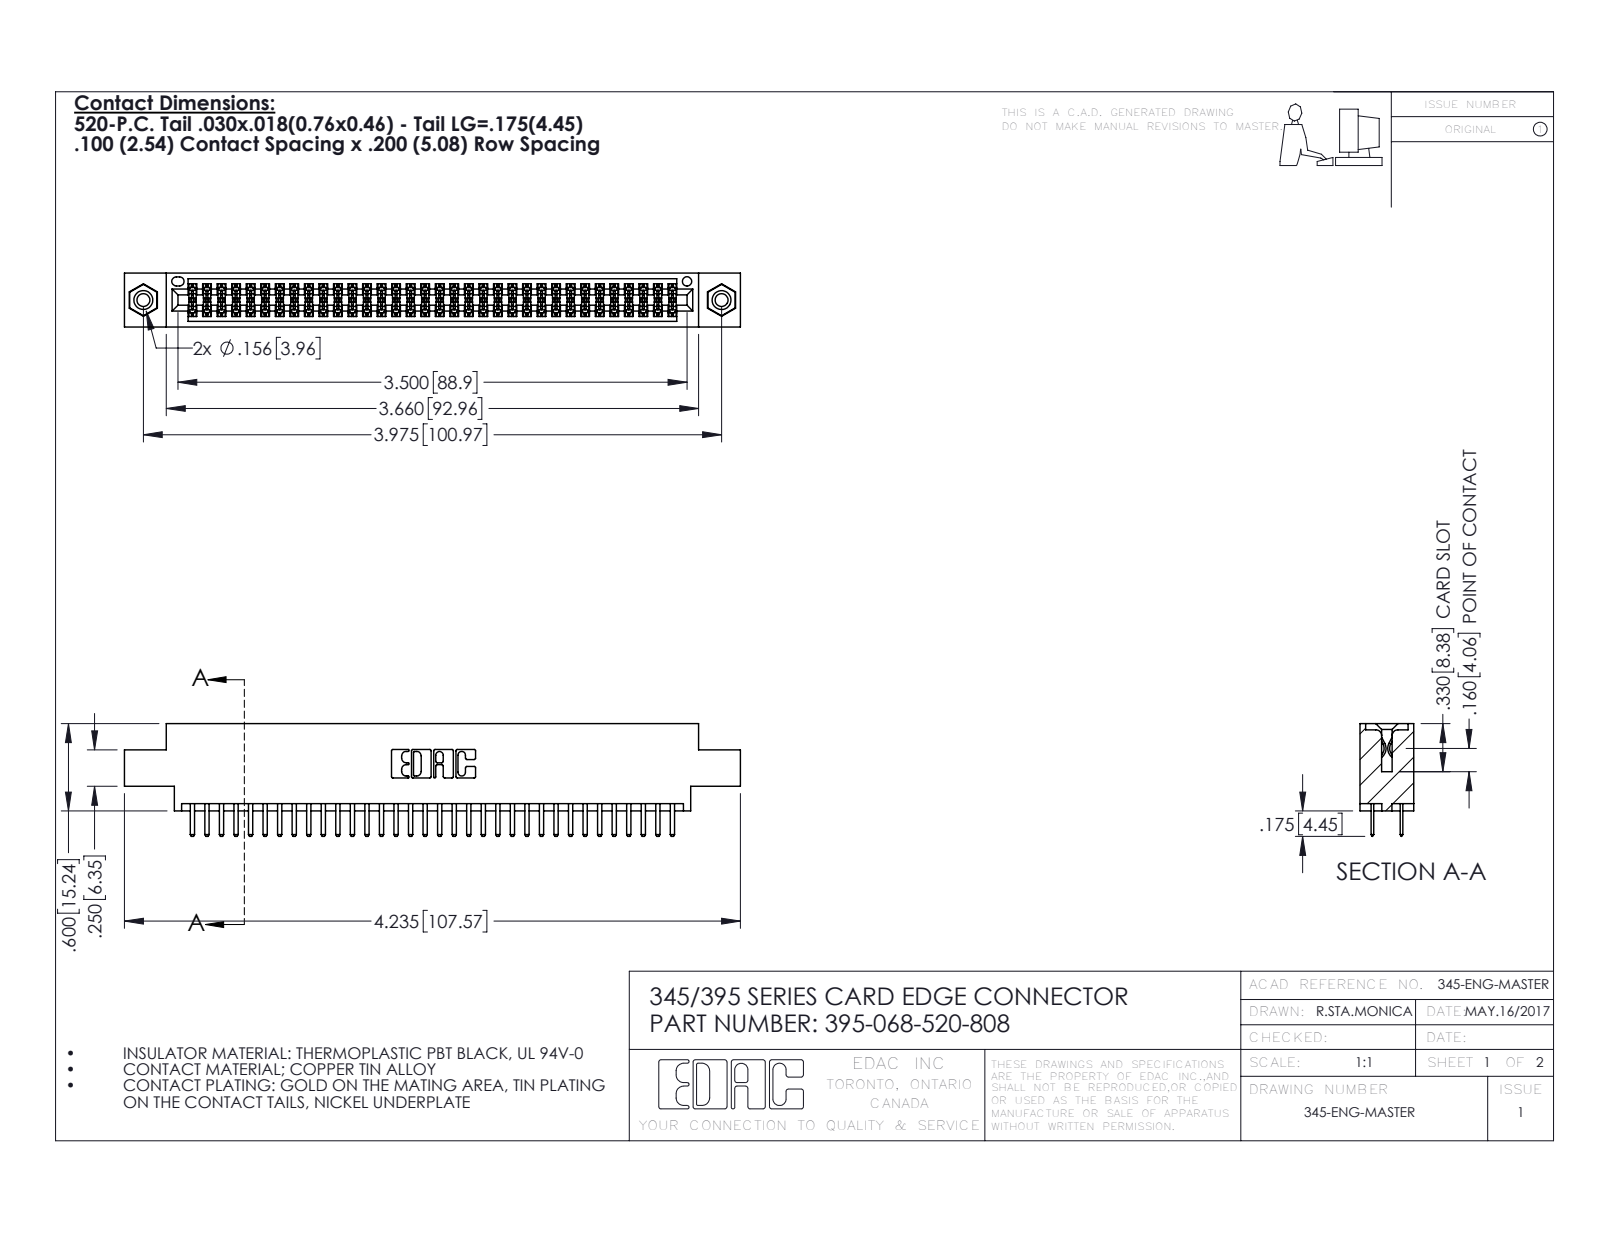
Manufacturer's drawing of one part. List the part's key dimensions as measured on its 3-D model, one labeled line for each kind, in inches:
Part name (STEP PRODUCT): 345 Part_0.170 Offset - 0.156 Dia-TI; 345-250-001_345-250-003-102; 395-068-520-808; 345-292-001_345-293-120
STEP written by: SolidWorks 2016 (CONFIG_CONTROL_DESIGN)
Units: inches
Bodies: 71 solids, 3862 faces (2496 planar, 1350 cylindrical, 16 other)
Overall size (bounding box): 4.235 × 0.775 × 0.37
Volume: 0.624 in³ · Surface area: 23.33 in²
Round holes (diameter × count): ⌀0.089 ×2, ⌀0.125 ×2, ⌀0.156 ×2, ⌀0.064 ×1
Round bosses / shafts (diameter × count): ⌀0.155 ×2
Partial cylindrical surfaces — rounded edges, fillets, slot ends (radius × count): R0.006 ×102, R0.01 ×72, R0.01 ×22, R0.007 ×6, R0.031 ×6, R0.026 ×3, R0.014 ×2, R0.019 ×2
Main face-to-face distances: 0.072, 0.298, 0.2, 0.37, 0.098, 0.272, 0.025, 0.225, 0.022, 0.175
Hole centre spacings: 0.27, 3.74, 3.975
